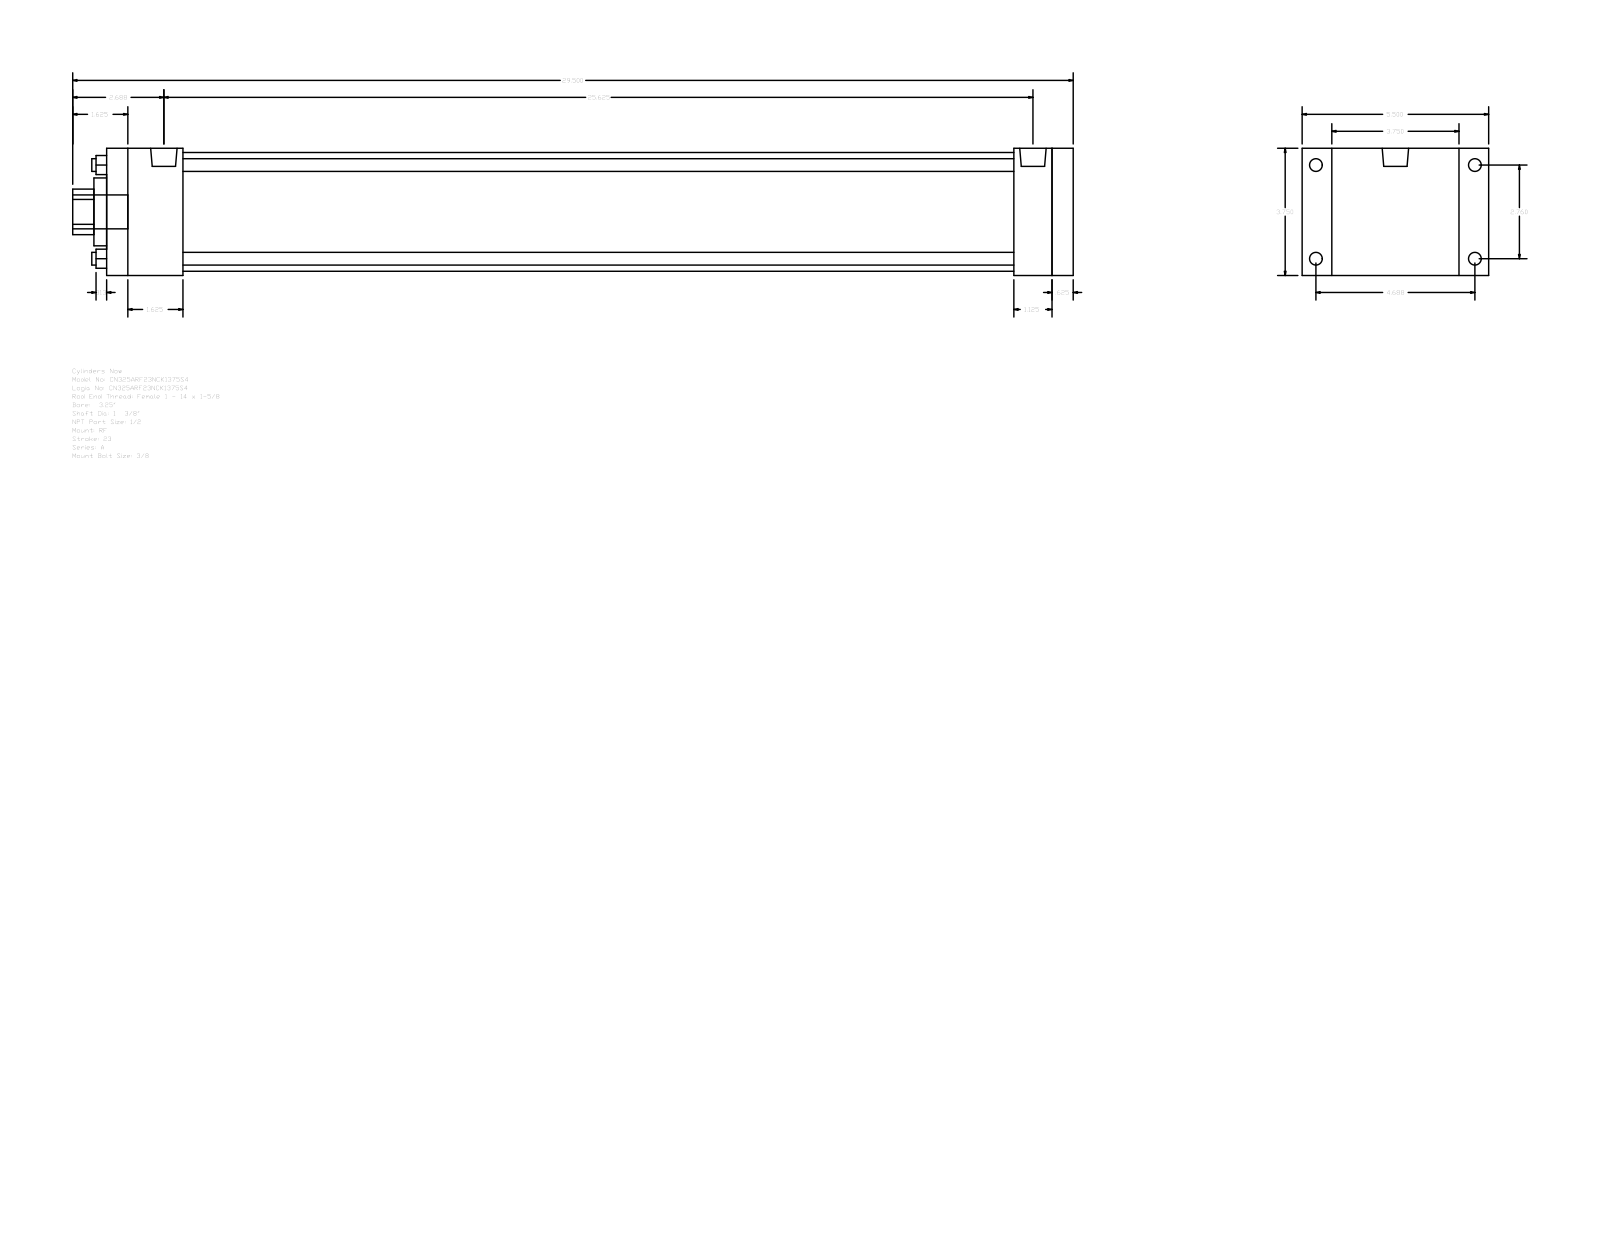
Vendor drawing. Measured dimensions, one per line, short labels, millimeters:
name: A_RF__0325_1.375
written by: GSSL Pune (CONFIG_CONTROL_DESIGN)
unit: mm
bodies: 0 solids, 92 faces (64 planar, 28 cylindrical, 0 other)
size: 749.3 × 139.7 × 95.25
holes: 4× ⌀9.53, 1× ⌀34.92, 1× ⌀50.8, 1× ⌀88.9
bosses: 4× ⌀9.53, 4× ⌀8.73, 2× ⌀19.77, 1× ⌀25.4
rounds: 1× R17.06
face distances: 95.24, 723.9, 15.88, 708.02, 22.23, 117.47, 28.57, 679.45, 44.45, 57.15
hole spacings: 49.57, 70.1, 99.14
